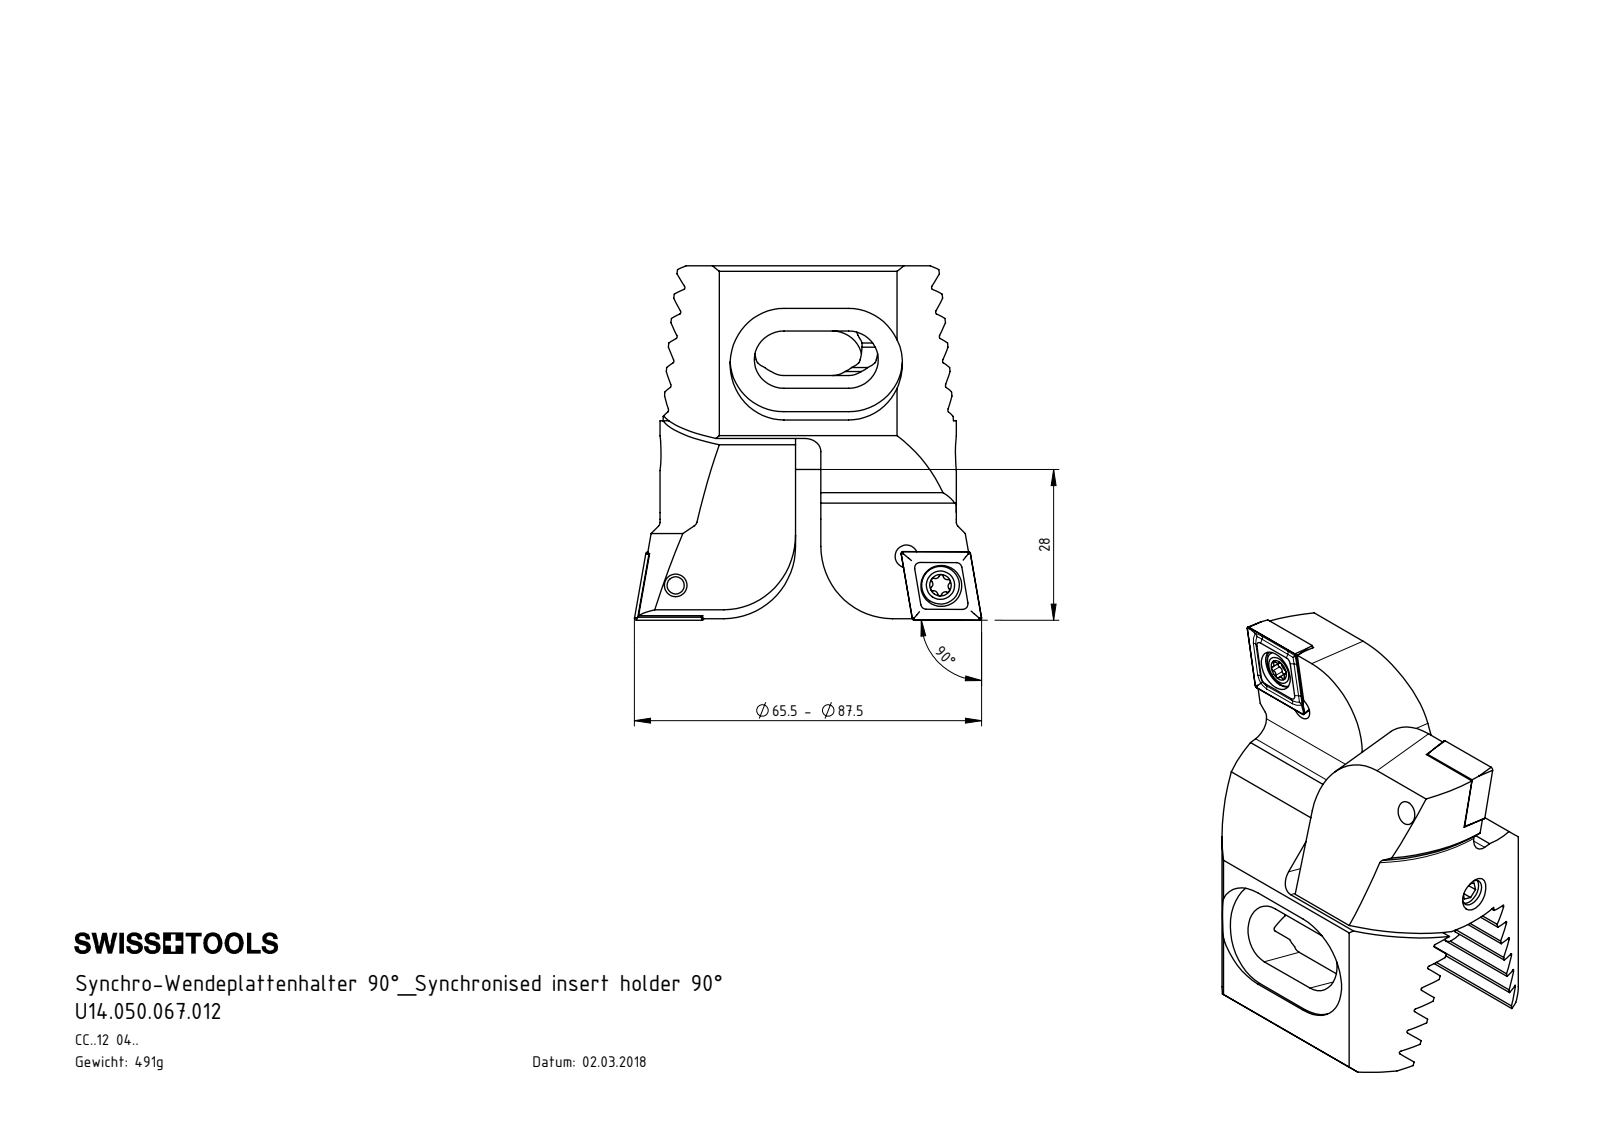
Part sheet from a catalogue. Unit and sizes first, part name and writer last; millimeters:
Units: millimetres
Overall size (bounding box): 65.75 × 64.42 × 44
Round holes (diameter × count): ⌀4.2 ×4, ⌀1 ×3, ⌀3.3 ×3, ⌀5.5 ×2, ⌀7.6 ×2, ⌀5 ×1
Round bosses / shafts (diameter × count): ⌀4 ×3, ⌀7 ×2, ⌀5 ×2, ⌀17 ×1, ⌀6 ×1, ⌀3.8 ×1
Partial cylindrical surfaces — rounded edges, fillets, slot ends (radius × count): R0.34 ×12, R0.39 ×12, R0.69 ×12, R1 ×8, R3 ×4, R5.5 ×4, R10 ×4, R13.3 ×2
Main face-to-face distances: 4.07, 8.14, 12.21, 16.28, 20.35, 4.85, 17.24, 1, 7.12, 21.7
Hole centre spacings: 8.29, 3, 8.49, 8.5, 14.99, 15, 15.3, 28.36
Volume: 62 569 mm³ · Surface area: 24 121 mm²
Bodies: 11 solids, 381 faces (187 planar, 98 cylindrical, 96 other)
Part name (STEP PRODUCT): Z55.WCC.B11.037; Z55-ER3.001.052_A; CCMT120404; Z55-WCC.003.037_A (+4 more)
STEP written by: SolidWorks 2017 (AUTOMOTIVE_DESIGN)
